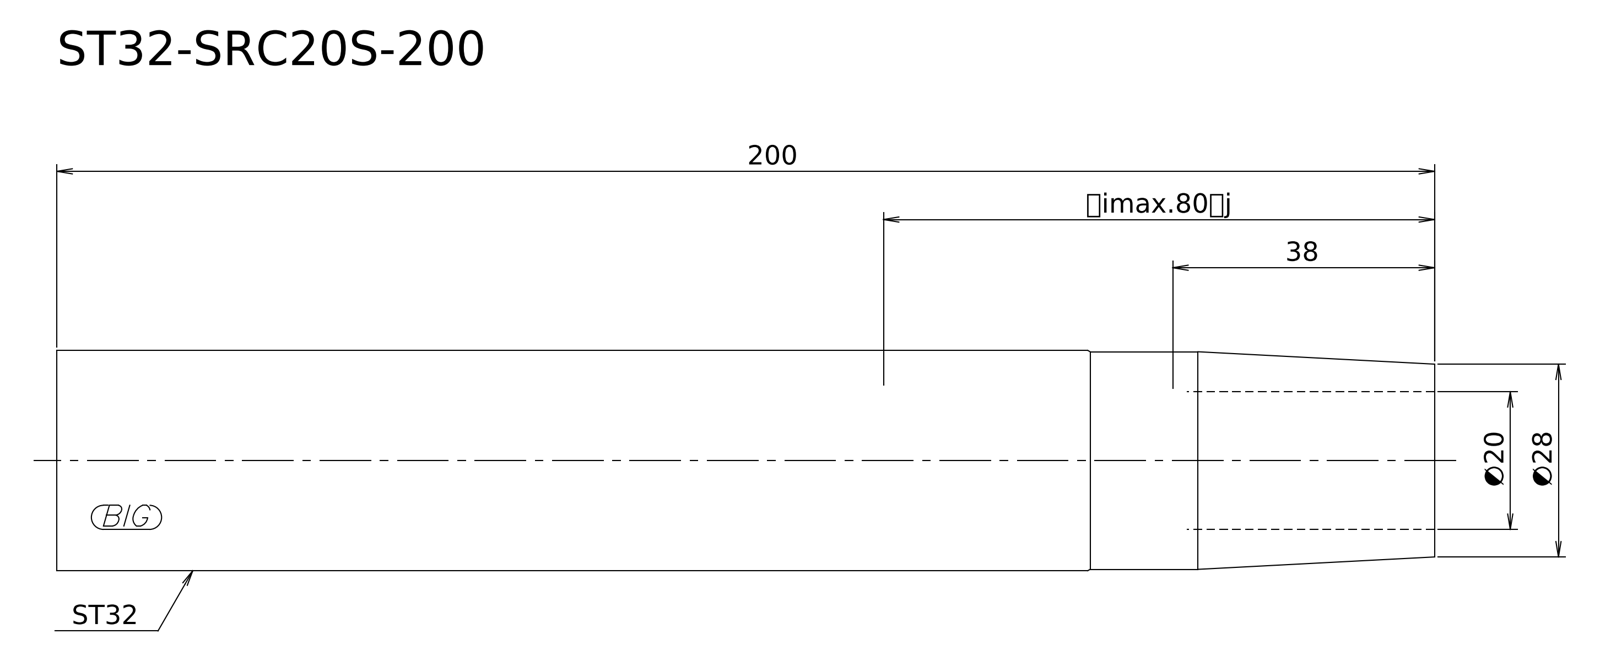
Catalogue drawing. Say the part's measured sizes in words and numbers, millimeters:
Its 3-D file was written by "Kubotek KeyCreator V8.5.1 (14335) (CONFIG_CONTROL_DESIGN)". It is 1 solid with 6 faces: 2 planar, 2 cylindrical and 2 other. Overall it measures 200 by 32 by 32 millimeters. Its volume is 156 895 cubic millimeters and its surface area 21 279 square millimeters. Round bosses or shafts: 1 of diameter 32, 1 of diameter 31.6. The main face-to-face distances are 200.
